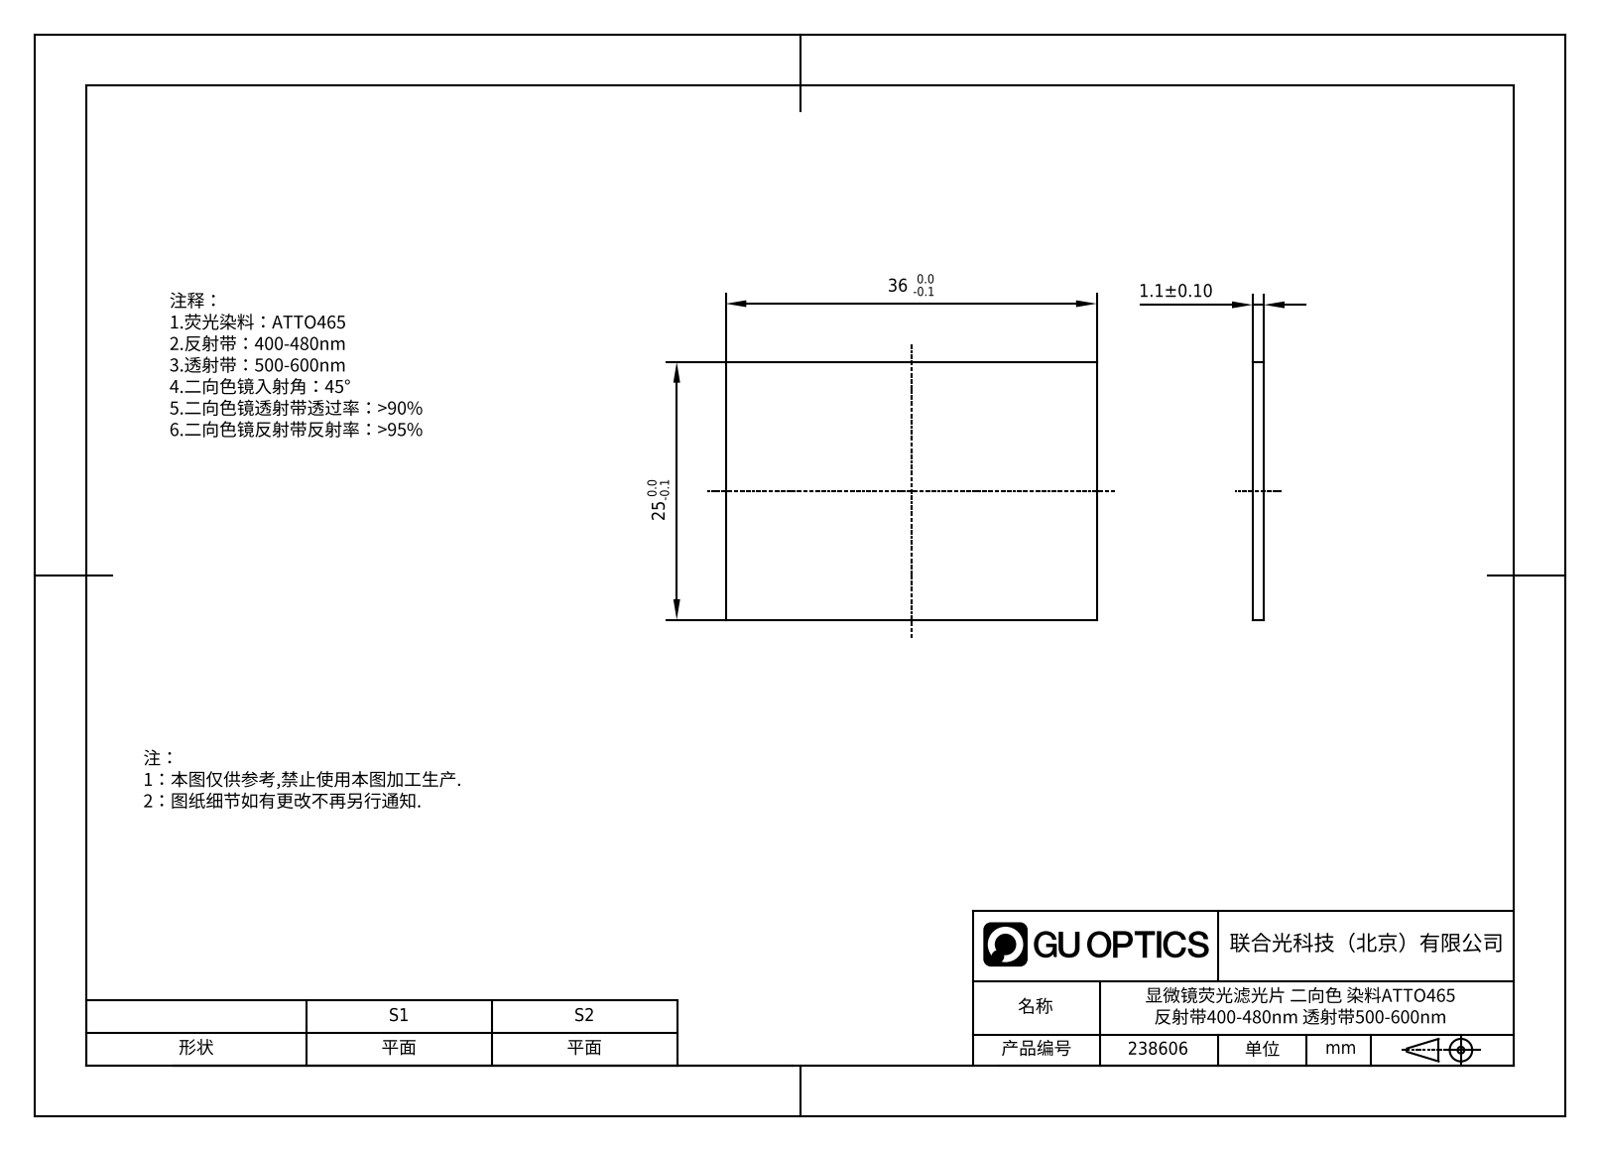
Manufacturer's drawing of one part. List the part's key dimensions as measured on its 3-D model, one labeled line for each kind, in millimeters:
Part name (STEP PRODUCT): GDMLPH-490-25x36
STEP written by: SolidWorks 2022 (AUTOMOTIVE_DESIGN)
Units: millimetres
Bodies: 1 solid, 6 faces (6 planar, 0 cylindrical, 0 other)
Overall size (bounding box): 36 × 25 × 1.1
Volume: 990 mm³ · Surface area: 1 934 mm²
Main face-to-face distances: 1.1, 25, 36
